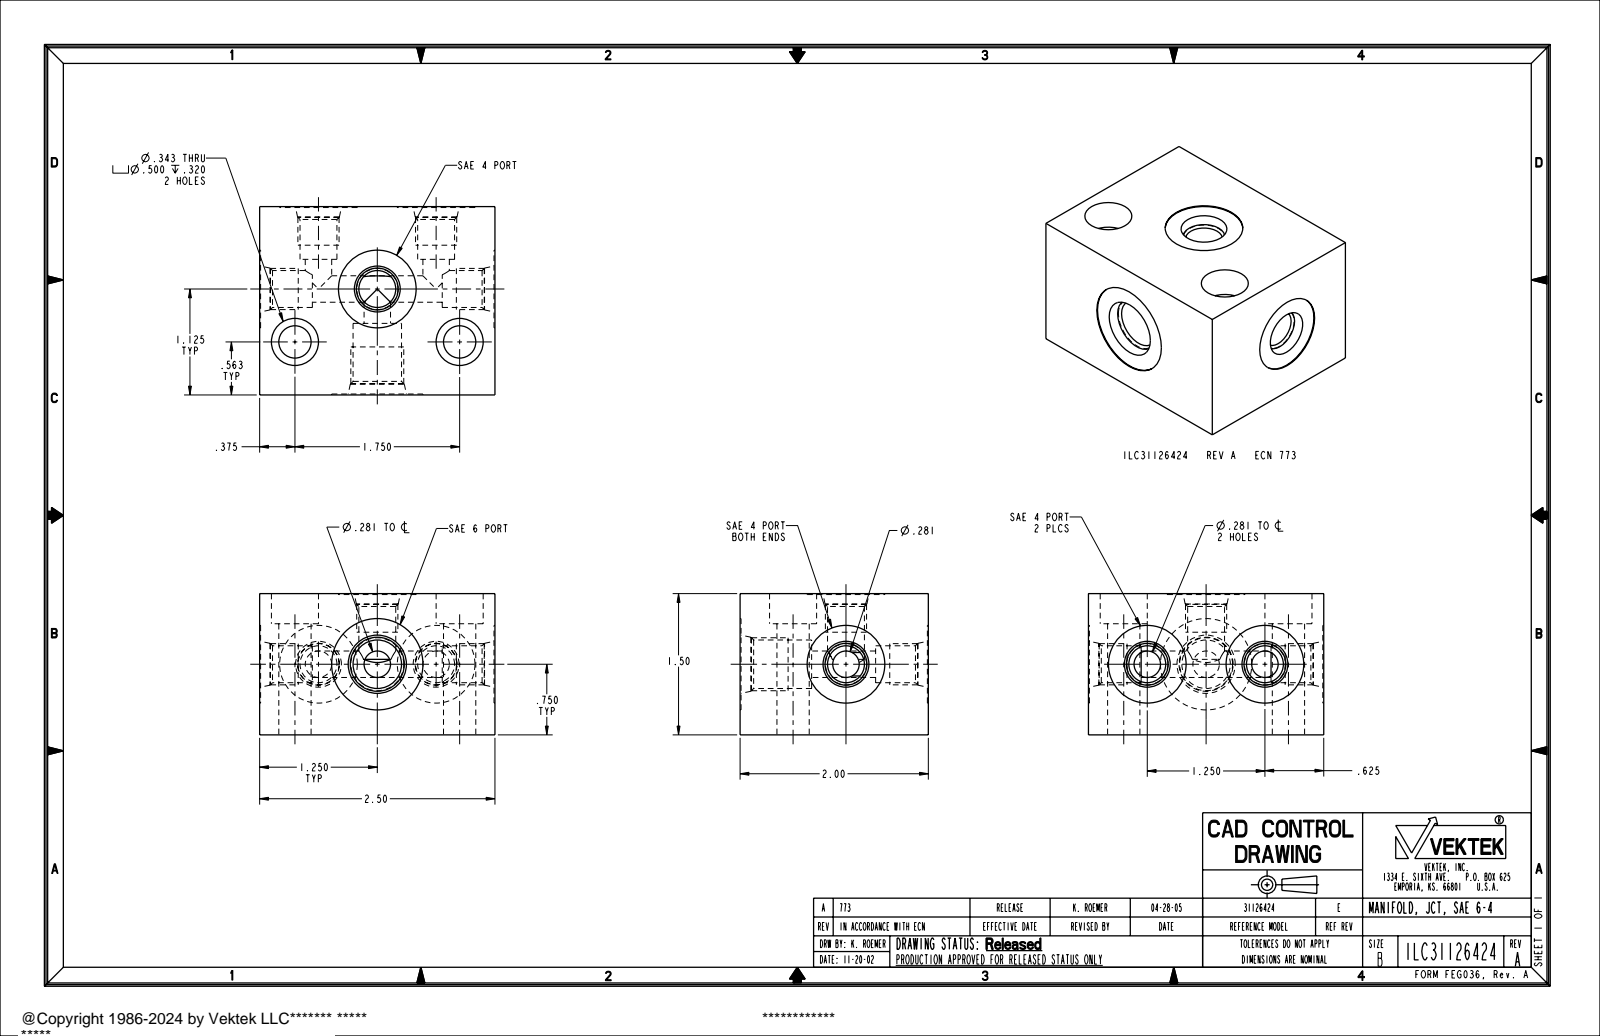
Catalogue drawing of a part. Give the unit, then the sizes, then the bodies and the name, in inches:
Units: inches
Overall size (bounding box): 2.5 × 2 × 1.5
Round holes (diameter × count): ⌀0.281 ×4, ⌀0.392 ×4, ⌀0.825 ×4, ⌀0.343 ×2, ⌀0.5 ×2, ⌀0.515 ×1, ⌀0.97 ×1
Round bosses / shafts (diameter × count): ⌀0.437 ×4, ⌀0.563 ×1
Main face-to-face distances: 1.5, 2, 2.5, 1.99, 2.49, 1.98, 2.48, 1.49, 1.18, 0.31
Hole centre spacings: 0.625, 1.04, 1.25, 1.75
Volume: 6.466 in³ · Surface area: 35.32 in²
Bodies: 1 solid, 105 faces (25 planar, 53 cylindrical, 27 other)
Part name (STEP PRODUCT): ILC31126424
STEP written by: PRO/ENGINEER BY PARAMETRIC TECHNOLOGY CORPORATION, 2004290 (AUTOMOTIVE_DESIGN_CC2)
